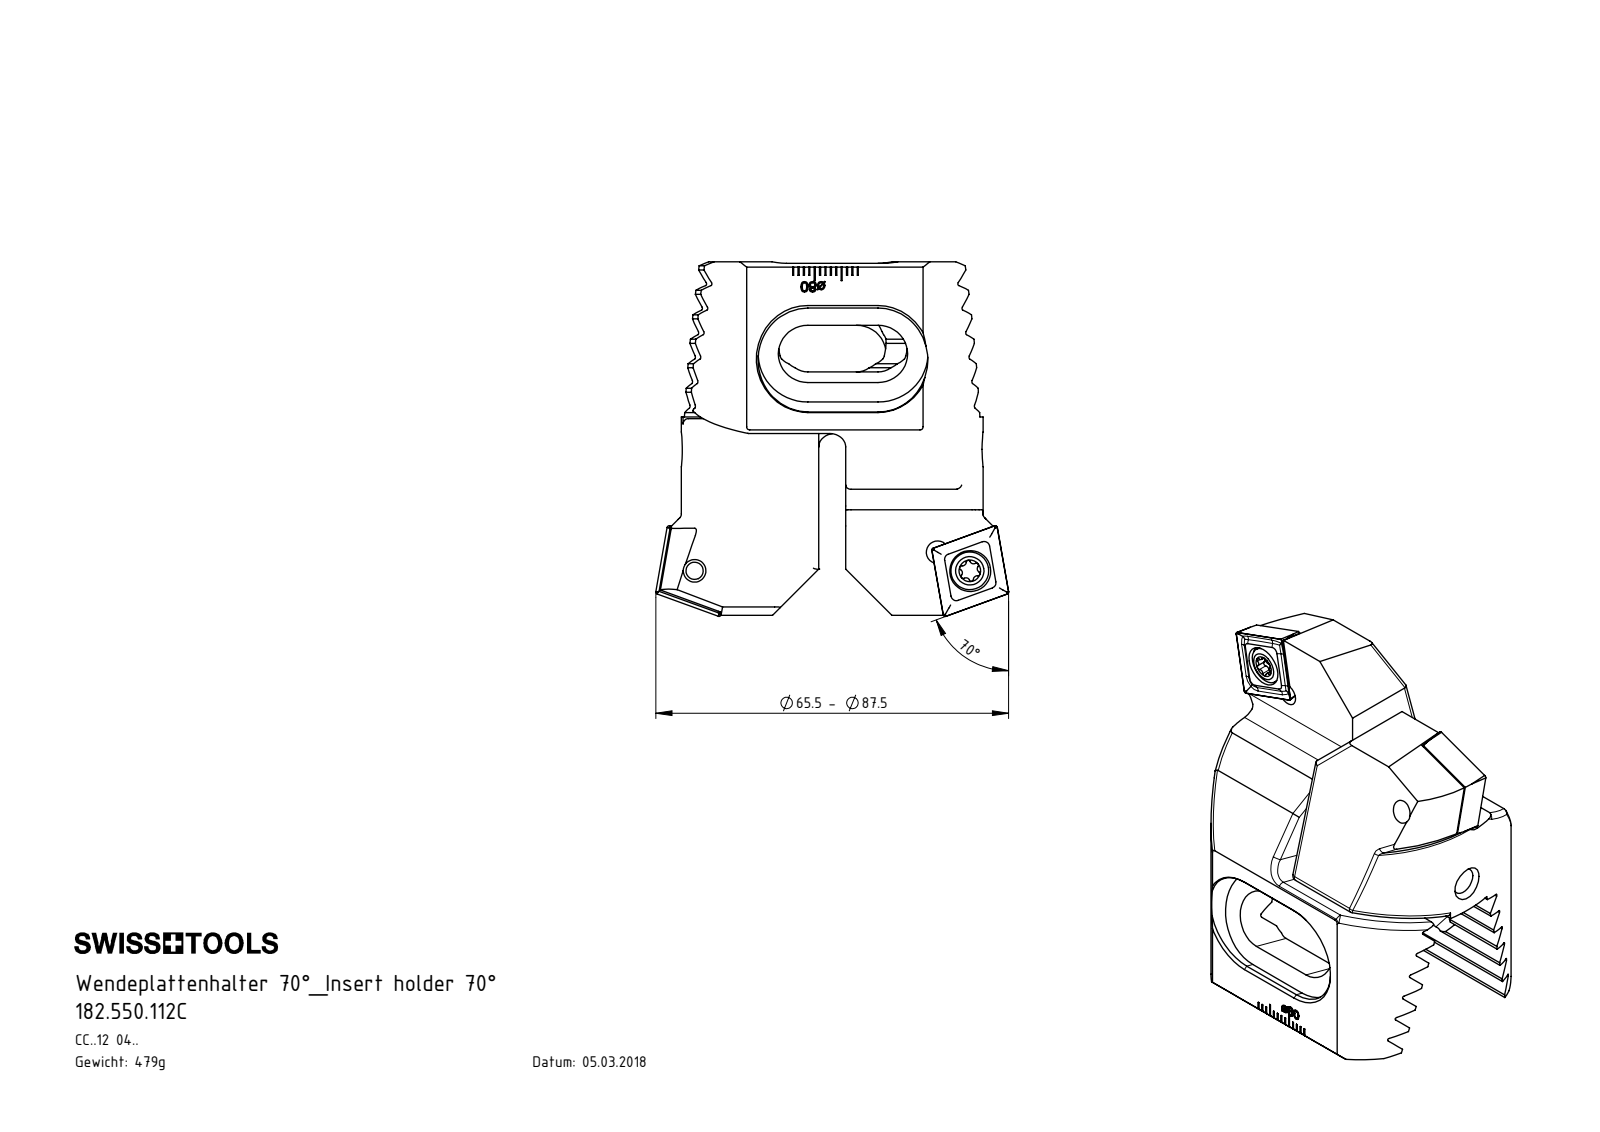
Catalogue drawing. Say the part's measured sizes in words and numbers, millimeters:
The part is named "Z55-ER3.001.020; 182.550.112C; WCC-ER2.001.010_A; Z55-xxx.001.037_C_CC 12 70ø (+1 more)". Its 3-D file was written by "SolidWorks 2017 (CONFIG_CONTROL_DESIGN)". It is 8 solids with 692 faces: 336 planar, 132 cylindrical and 224 other. Overall it measures 65.8 by 65.5 by 44.2 millimeters. Its volume is 61 870 cubic millimeters and its surface area 22 753 square millimeters. Round holes: 4 of diameter 4.2, 2 of diameter 2, 2 of diameter 5.5, 2 of diameter 7.6, 1 of diameter 5. Round bosses or shafts: 2 of diameter 7, 2 of diameter 5, 1 of diameter 6, 1 of diameter 4. Partial cylindrical surfaces (rounded edges, fillets, slot ends): 14 of radius 1, 12 of radius 0.34, 12 of radius 0.39, 8 of radius 0.69, 6 of radius 3, 4 of radius 0.69, 4 of radius 5.5, 4 of radius 9.25. The main face-to-face distances are 4.07, 8.14, 12.21, 16.28, 20.35, 7.85, 1.69, 21.8, 22.4, 5. The hole center spacings are 6.89, 6.98, 16, 45.25, 45.33, 51.16, 30.9, 39.16.
